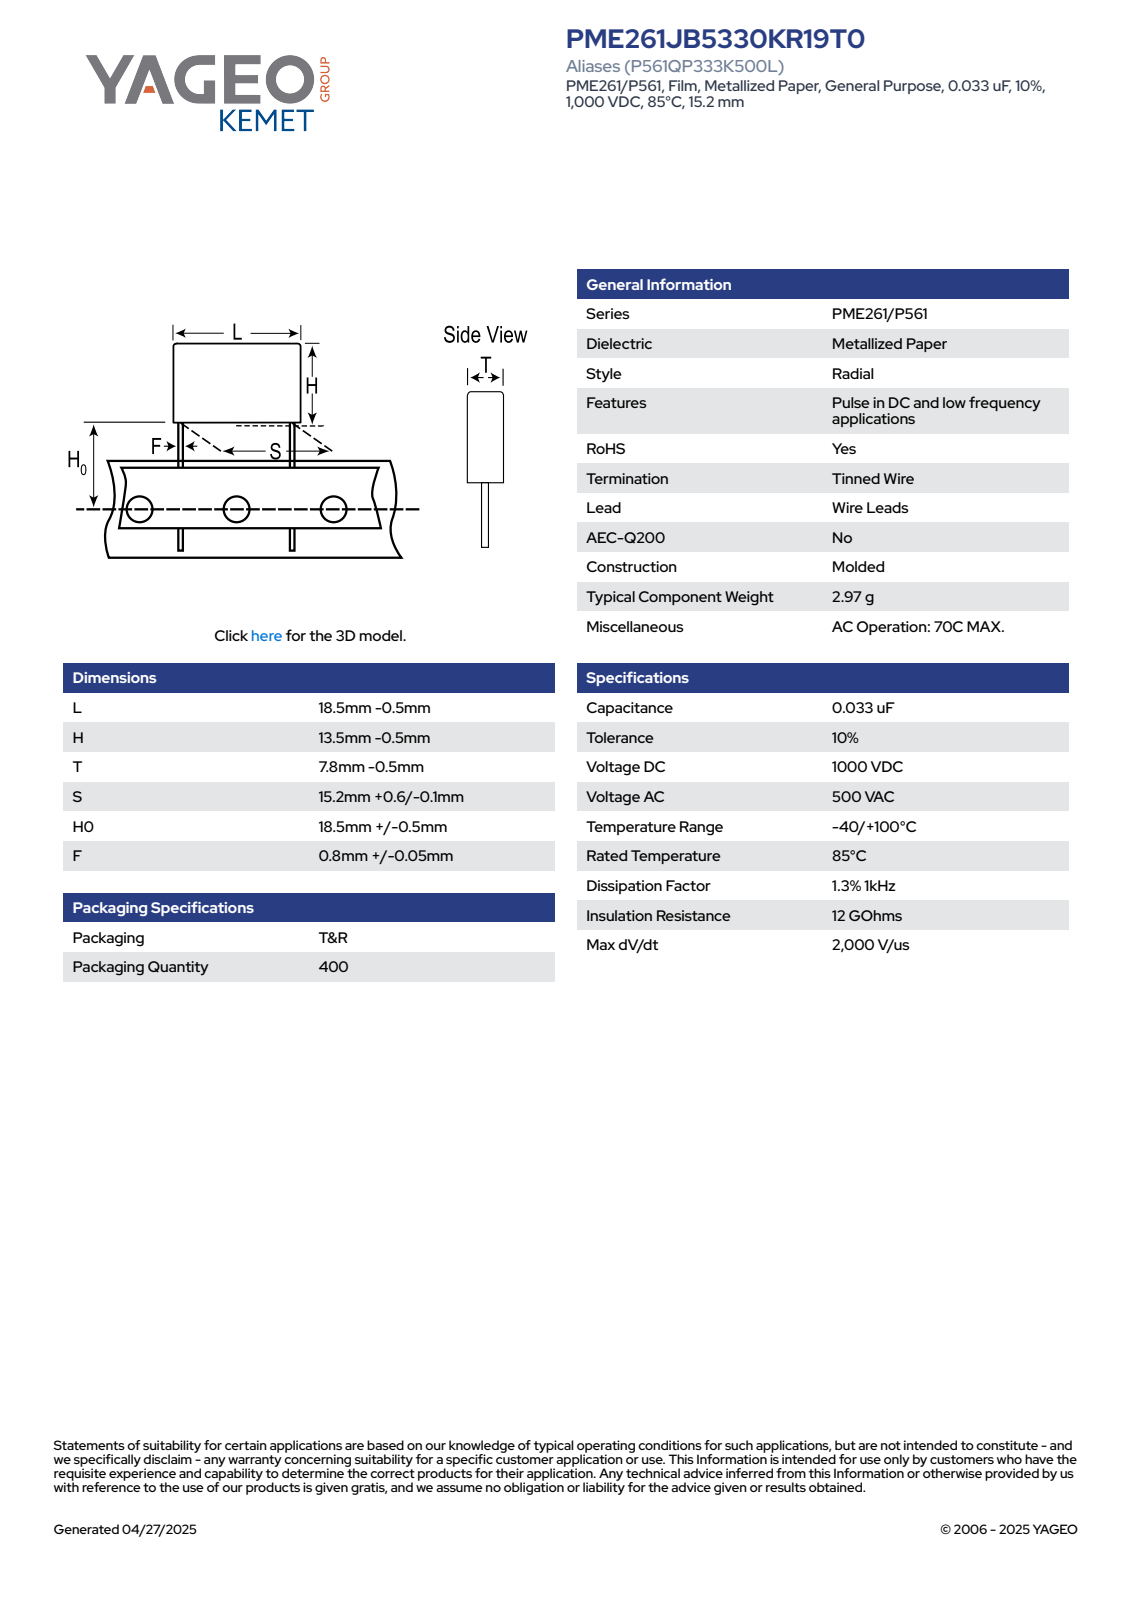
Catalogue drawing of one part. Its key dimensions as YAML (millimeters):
part_name: "CFR_MOLDED_18.5X13.5X7.8_L18H13T7.3S15.2H019F0.85"
step_written_by: "SolidWorks 2014 (AUTOMOTIVE_DESIGN)"
units: millimeters
bodies: {solids: 4, faces: 73, planar: 65, cylindrical: 8, other: 0}
overall_size: [32, 18, 7.3]
volume: 1727
surface_area: 1027
round_bosses_or_shafts:
  - {diameter: 0.85, count: 2}
partial_cylinders:
  - {radius: 0.5, count: 4}
face_to_face_distances: [7.3, 13, 18, 19, 32, 26.06, 7.06, 5.94, 24.45, 5.45]
